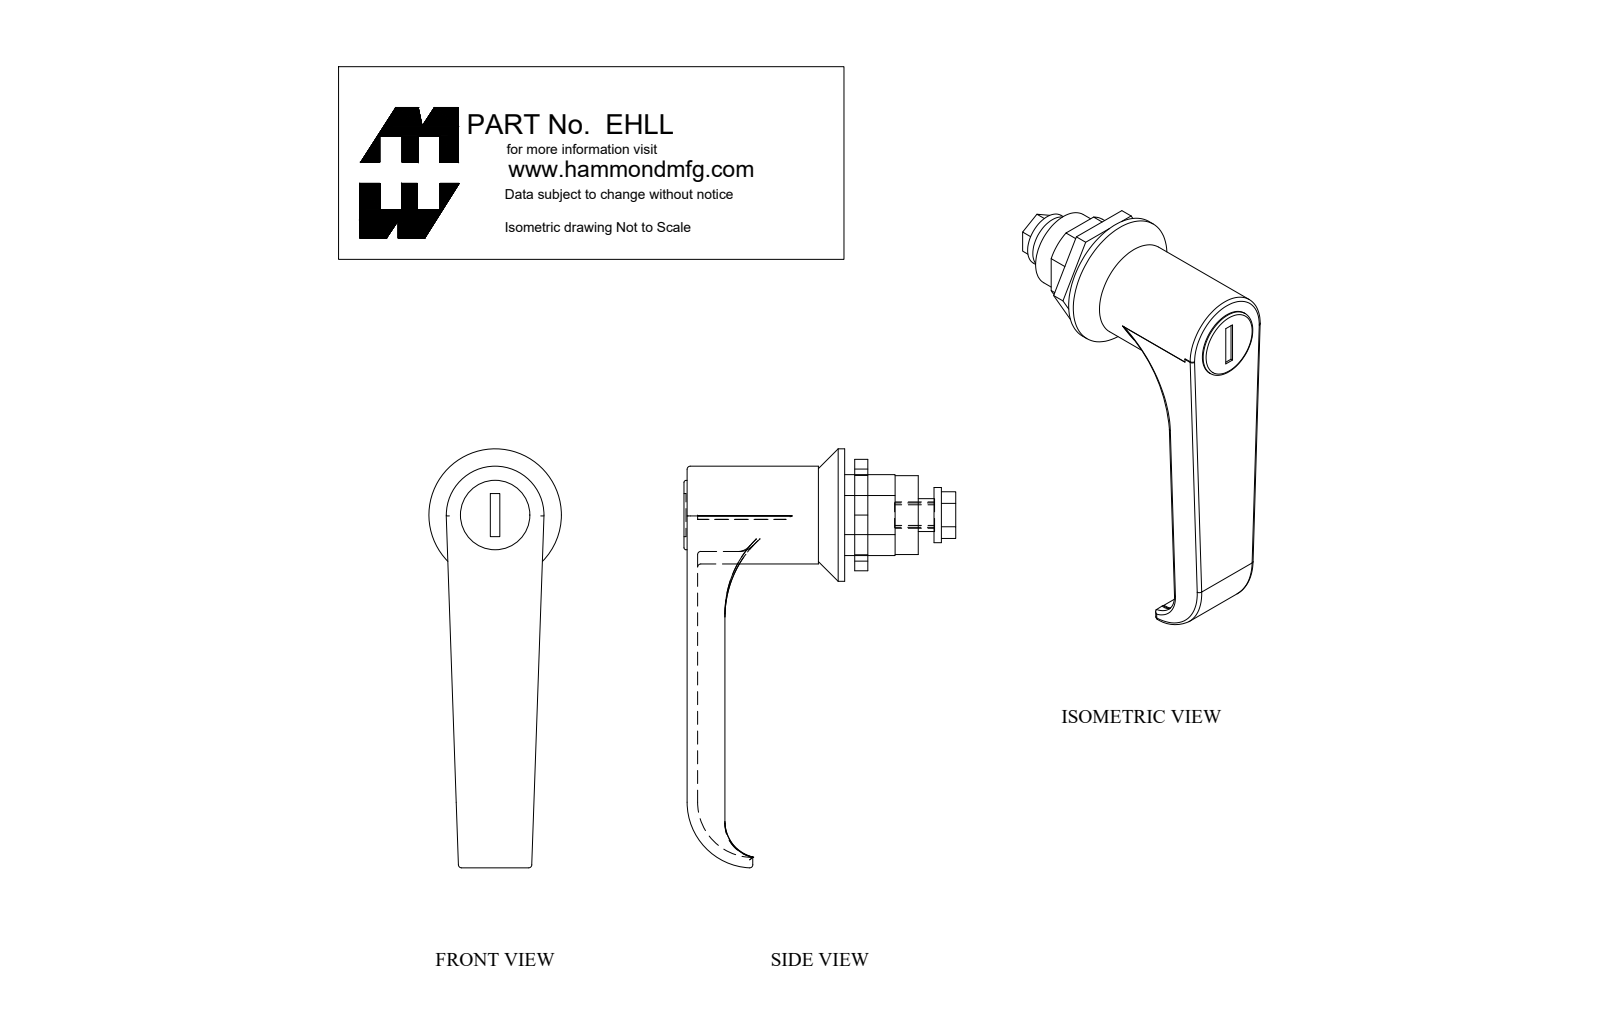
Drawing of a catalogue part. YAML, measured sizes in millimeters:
part_name: "EHLL_Default"
step_written_by: "SolidWorks 2018 (CONFIG_CONTROL_DESIGN)"
units: millimeters
bodies: {solids: 3, faces: 134, planar: 54, cylindrical: 44, other: 36}
overall_size: [101.2, 65.7, 32]
volume: 32790
surface_area: 13110
round_holes:
  - {diameter: 5, count: 1}
  - {diameter: 19.2, count: 1}
round_bosses_or_shafts:
  - {diameter: 32, count: 1}
  - {diameter: 23.6, count: 1}
  - {diameter: 19.1, count: 1}
  - {diameter: 16.8, count: 1}
  - {diameter: 13.3, count: 1}
  - {diameter: 5.9, count: 1}
partial_cylinders:
  - {radius: 0.8, count: 15}
  - {radius: 8.3, count: 1}
  - {radius: 8.9, count: 1}
  - {radius: 10.8, count: 1}
  - {radius: 13.3, count: 1}
  - {radius: 15.9, count: 1}
  - {radius: 25.3, count: 1}
  - {radius: 25.4, count: 1}
face_to_face_distances: [2.5, 5.6, 35.6, 38.1, 41.1, 2.5, 43.7, 3.2, 2.4, 38]
